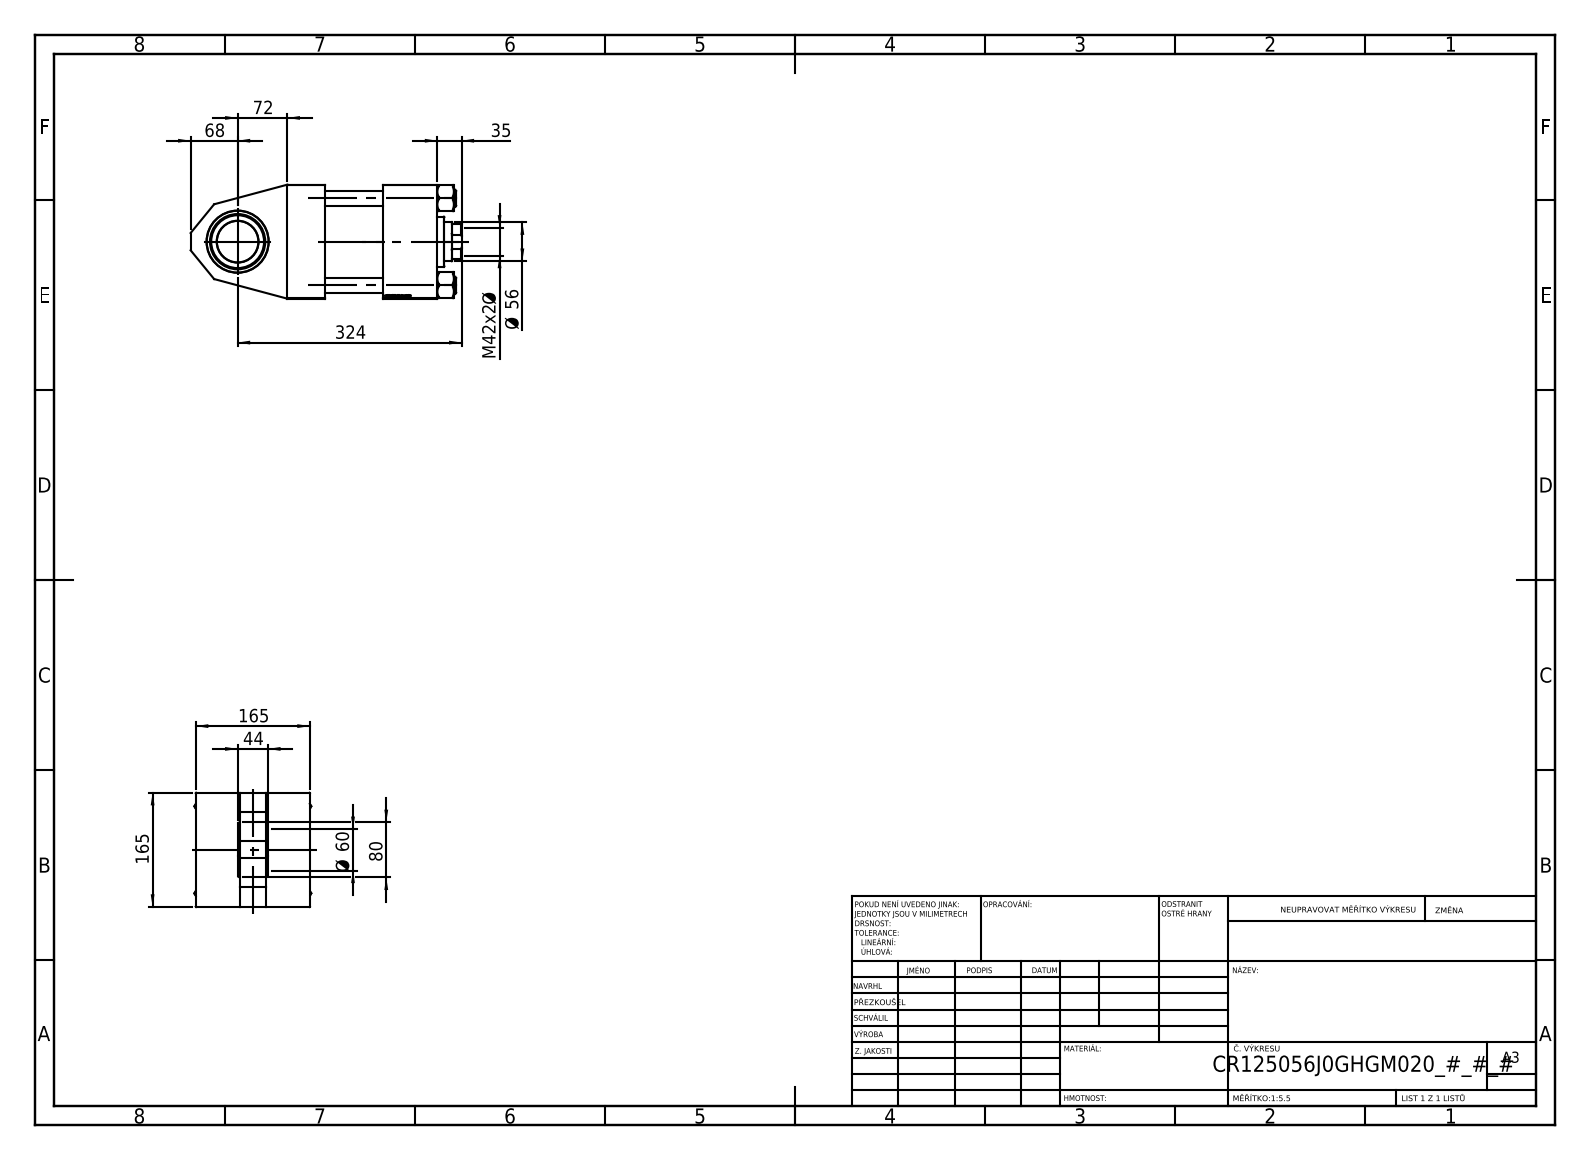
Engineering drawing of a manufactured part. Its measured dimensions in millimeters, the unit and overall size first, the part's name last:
Units: millimetres
Overall size (bounding box): 392 × 169.14 × 165
Round holes (diameter × count): ⌀22 ×4, ⌀2.5 ×2, ⌀7 ×2, ⌀32.24 ×2, ⌀45 ×2, ⌀40.5 ×1, ⌀56 ×1, ⌀59 ×1, ⌀60 ×1, ⌀90 ×1, ⌀96 ×1, ⌀125 ×1
Round bosses / shafts (diameter × count): ⌀25 ×4, ⌀131 ×1, ⌀72 ×1
Partial cylindrical surfaces — rounded edges, fillets, slot ends (radius × count): R27 ×1
Main face-to-face distances: 165, 162, 63.5, 101.5, 55, 217, 78, 139, 84, 98
Hole centre spacings: 62.98, 89.02, 125.9, 139.02, 61, 178.05, 99.5, 122
Volume: 5 062 000 mm³ · Surface area: 572 912 mm²
Bodies: 12 solids, 1193 faces (564 planar, 89 cylindrical, 540 other)
Part name (STEP PRODUCT): V215CR_VCP_J; V215_VC_A; V215CR_TYCINKA_J; V215CR_J_VNITRNI_KROUZEK (+2 more)
STEP written by: SolidWorks 2019 (CONFIG_CONTROL_DESIGN)
